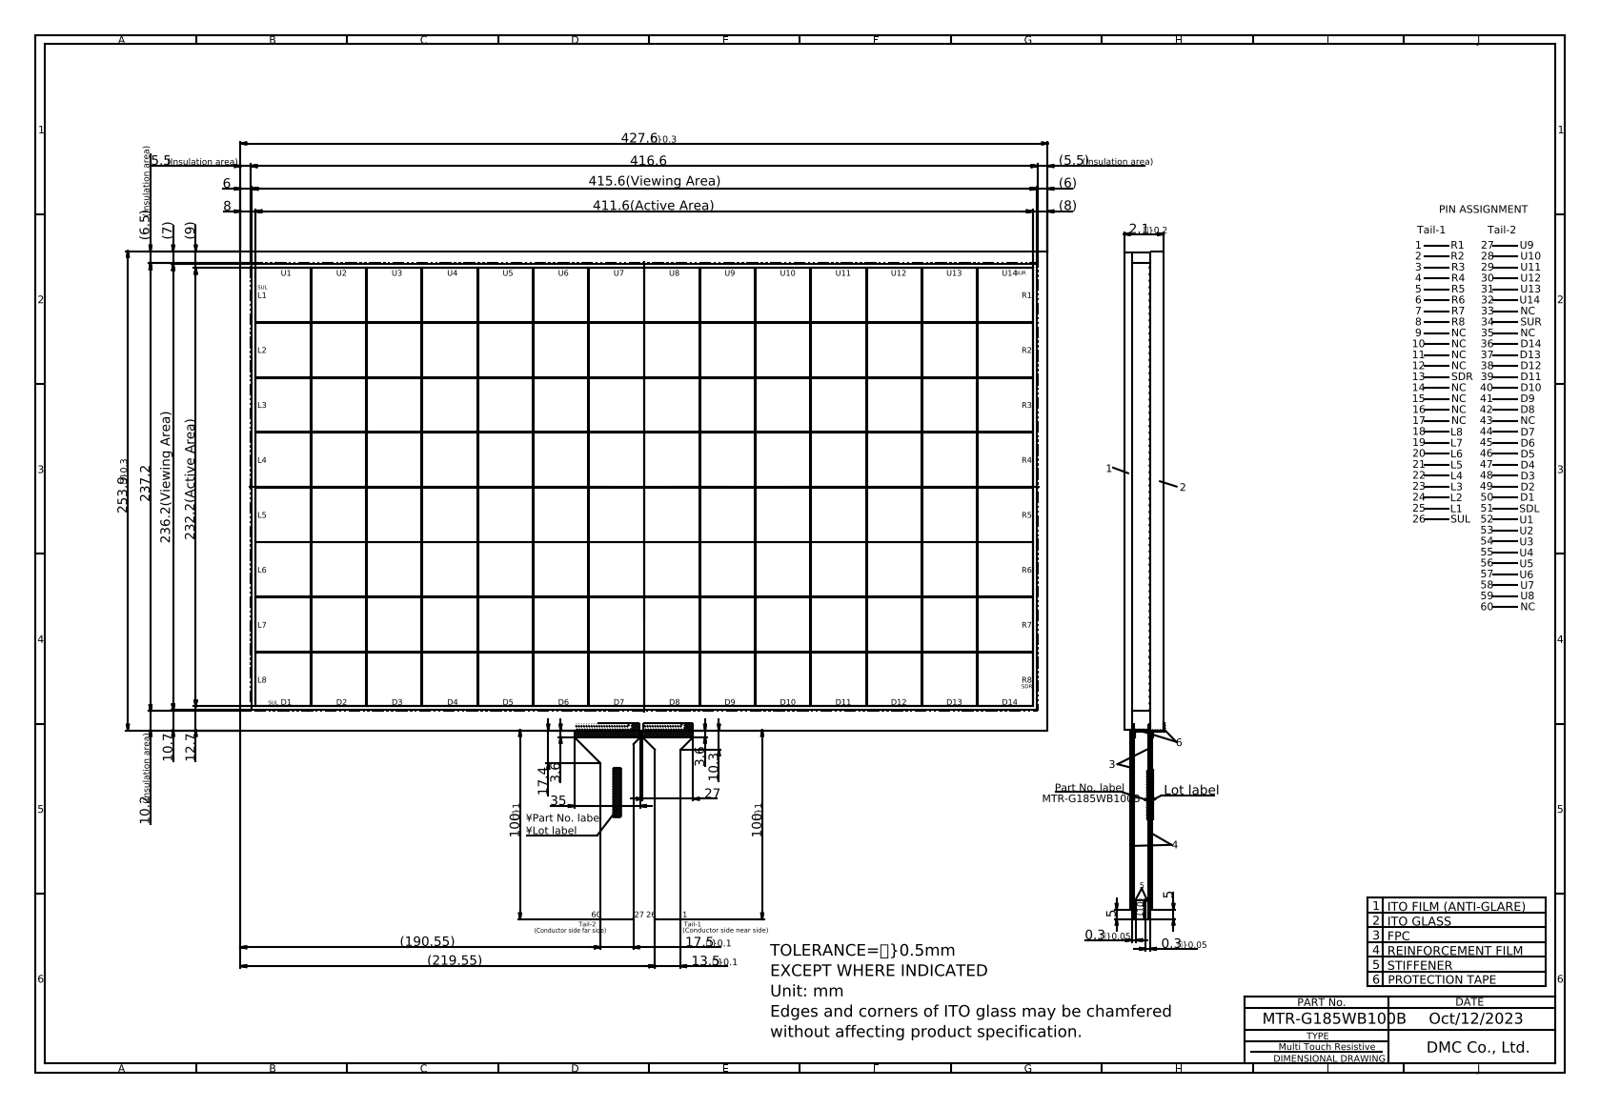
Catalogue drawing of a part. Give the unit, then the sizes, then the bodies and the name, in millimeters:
Units: millimetres
Overall size (bounding box): 598.64 × 404.68 × 2.2
Partial cylindrical surfaces — rounded edges, fillets, slot ends (radius × count): R1 ×8, R0.2 ×4
Main face-to-face distances: 2.1, 1.8, 1.9, 2, 253.9, 427.6, 0.4, 2.2, 0.5, 0.7
Volume: 228 146 mm³ · Surface area: 227 047 mm²
Bodies: 1 solid, 294 faces (282 planar, 12 cylindrical, 0 other)
Part name (STEP PRODUCT): MTR-G185WB100B
STEP written by: Autodesk Inventor 2020 (CONFIG_CONTROL_DESIGN)
